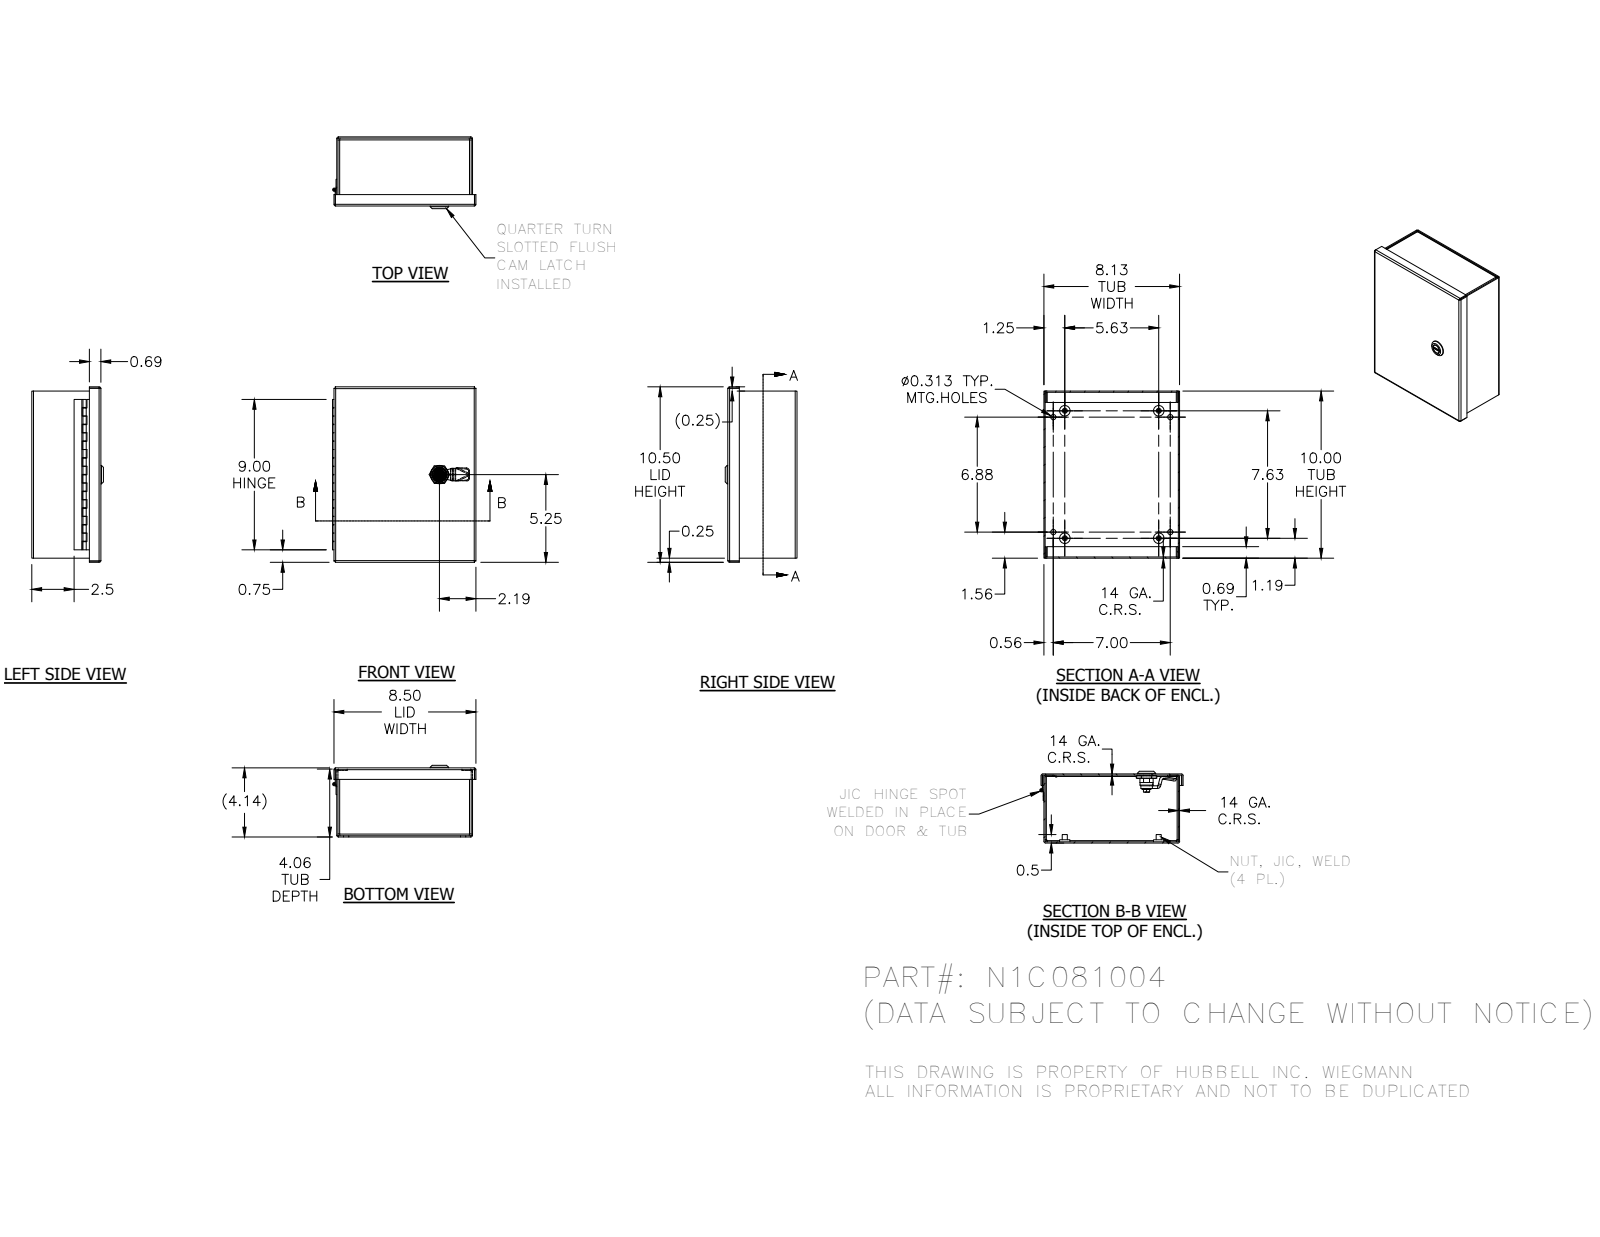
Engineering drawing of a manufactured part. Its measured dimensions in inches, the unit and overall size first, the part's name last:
Units: inches
Overall size (bounding box): 10.5 × 8.584 × 4.294
Round holes (diameter × count): ⌀0.156 ×4, ⌀0.313 ×4, ⌀0.116 ×1, ⌀0.197 ×1, ⌀0.315 ×1, ⌀0.394 ×1, ⌀0.402 ×1, ⌀0.634 ×1, ⌀0.802 ×1
Round bosses / shafts (diameter × count): ⌀0.625 ×4, ⌀0.3 ×4, ⌀1.102 ×1, ⌀0.866 ×1, ⌀0.78 ×1, ⌀0.63 ×1, ⌀0.598 ×1, ⌀0.531 ×1
Partial cylindrical surfaces — rounded edges, fillets, slot ends (radius × count): R0.012 ×30, R0.031 ×16, R0.105 ×16, R0.02 ×10, R0.157 ×4, R0.016 ×3, R0.039 ×1, R0.173 ×1
Main face-to-face distances: 0.074, 4.063, 3.989, 8.051, 4.137, 9.926, 7.977, 8.125, 0.148, 10
Hole centre spacings: 0.783, 6.324, 7.283, 9.613, 3.718, 3.882, 5.625, 6.204
Volume: 29.17 in³ · Surface area: 811.2 in²
Bodies: 19 solids, 695 faces (399 planar, 214 cylindrical, 82 other)
Part name (STEP PRODUCT): N1C_SMALL; N1C0804TB; N1C081004BLR; HFW3513 (+8 more)
STEP written by: Autodesk Inventor 2012 (AUTOMOTIVE_DESIGN)
